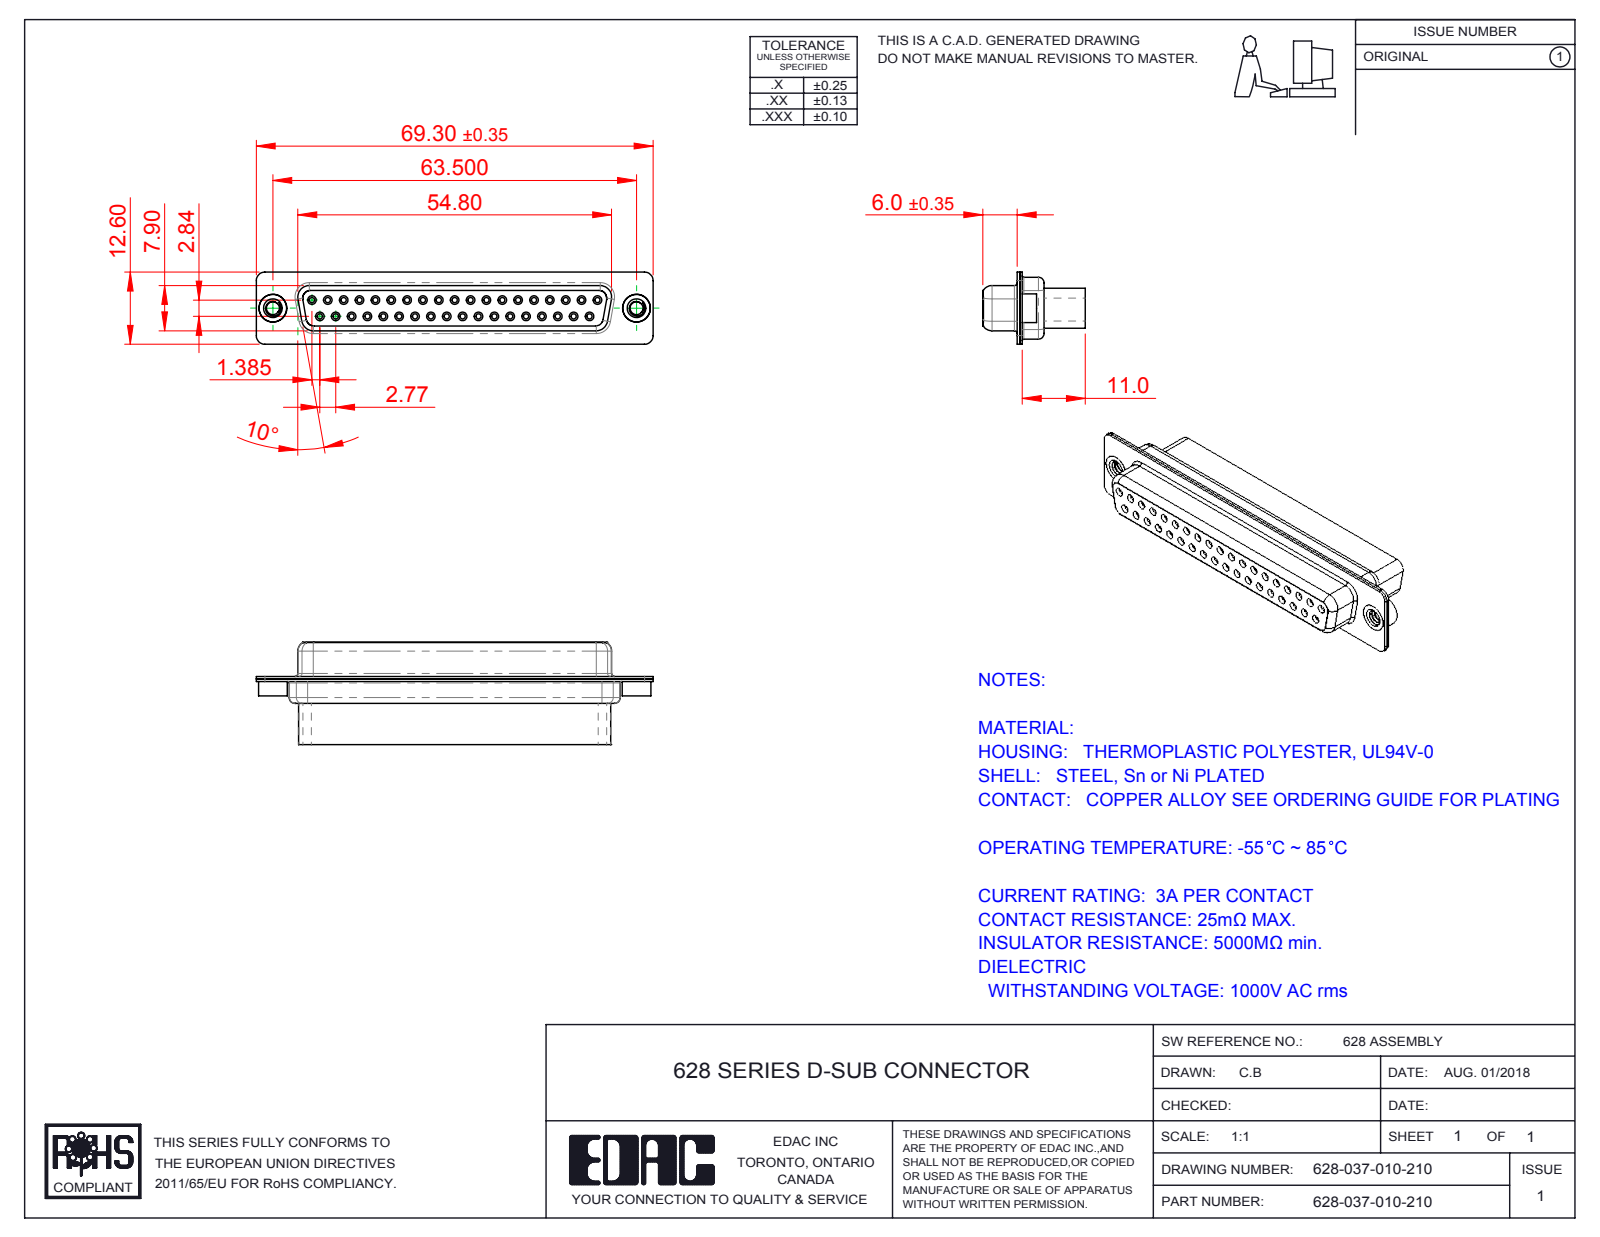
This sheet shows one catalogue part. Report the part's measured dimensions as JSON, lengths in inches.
{"part_name": "628 Shell Front_37 Contacts; 628-050-010-210; 628 Shell Rear_37 Contacts; 628 4-40 Threaded Rivet (+1 more)", "step_written_by": "SolidWorks 2016 (CONFIG_CONTROL_DESIGN)", "units": "inches", "bodies": {"solids": 5, "faces": 756, "planar": 178, "cylindrical": 431, "other": 147}, "overall_size": [2.728, 0.705, 0.496], "volume_in3": 0.406, "surface_area_in2": 16.96, "round_holes": [[0.035, 37], [0.059, 37], [0.079, 37], [0.067, 19], [0.063, 18], [0.089, 2], [0.157, 2], [0.159, 2], [0.191, 2]], "round_bosses_or_shafts": [[0.197, 2], [0.195, 2], [0.189, 2]], "partial_cylinders_radius": [[0.059, 16], [0.079, 12], [0.01, 4], [0.02, 4], [0.024, 4], [0.026, 4], [0.037, 4], [0.039, 4]], "face_to_face_distances": [0.016, 0.018, 0.26, 0.276, 0.075, 0.335, 0.033, 0.278, 0.293, 0.055], "hole_center_spacings": [0.124, 0.109, 0.218, 0.327, 0.198, 0.295, 0.436, 0.545]}
